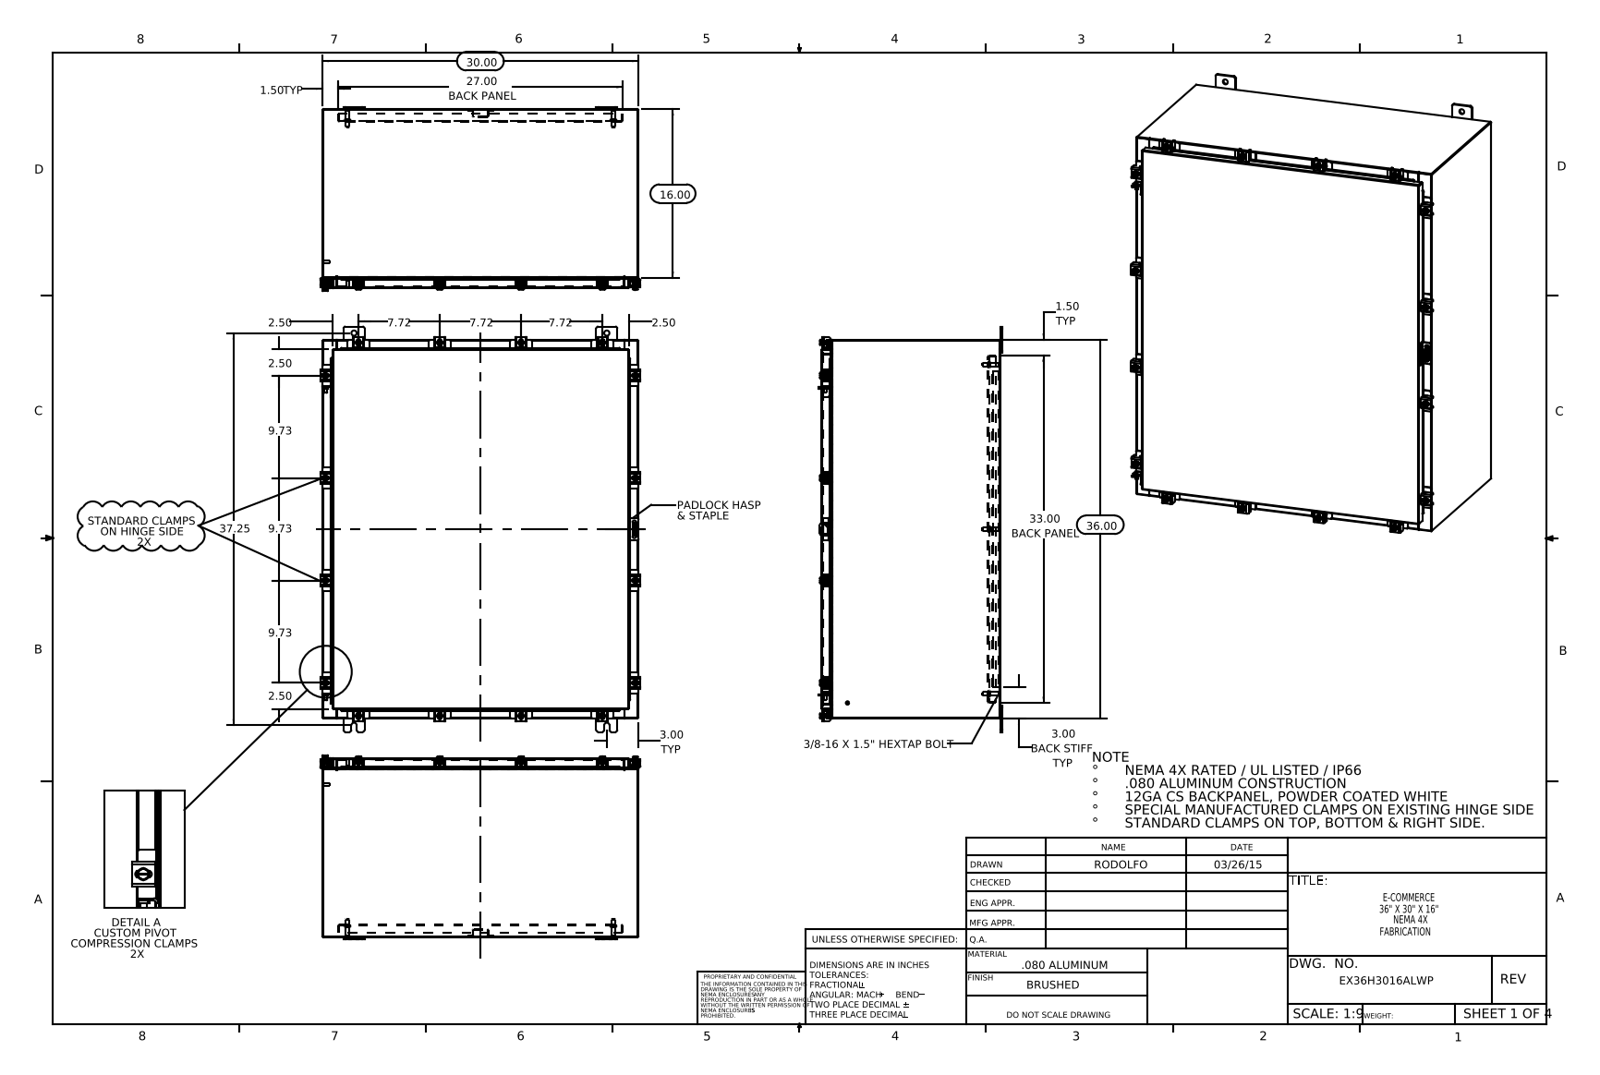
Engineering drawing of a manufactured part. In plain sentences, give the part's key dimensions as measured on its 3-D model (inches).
The part is named "N-WMT04X30402202210-00 22104005_DEFAULT; EX36H3016ALWP Padlock Staple; N-WMT04X30402202210-00 22101002; EX36H3016ALWP Special Clamp (+8 more)". Its 3-D file was written by "SolidWorks 2014 (CONFIG_CONTROL_DESIGN)". It is 104 solids with 2594 faces: 1371 planar, 1011 cylindrical and 212 other. Overall it measures 38.5 by 30.421 by 17.453 inches. Its volume is 459.9 cubic inches and its surface area 11 548 square inches. Round holes: 16 of diameter 0.213, 16 of diameter 0.26, 10 of diameter 0.5, 1 of diameter 0.125, 1 of diameter 0.25. Round bosses or shafts: 16 of diameter 0.5, 16 of diameter 0.25, 14 of diameter 0.399, 6 of diameter 0.625, 6 of diameter 0.375, 6 of diameter 0.33, 2 of diameter 0.315, 2 of diameter 0.236. Partial cylindrical surfaces (rounded edges, fillets, slot ends): 70 of radius 0.06, 32 of radius 0.141, 30 of radius 0.013, 30 of radius 0.12, 26 of radius 0.088, 24 of radius 0.19, 22 of radius 0.09, 21 of radius 0.05. The main face-to-face distances are 0.075, 16.9, 29.925, 16.826, 16.975, 0.104, 35.925, 1, 1.075, 15.826. The hole center spacings are 31.017, 2.347, 4.44, 5.299, 9.73, 10.964, 13.241, 14.744.
